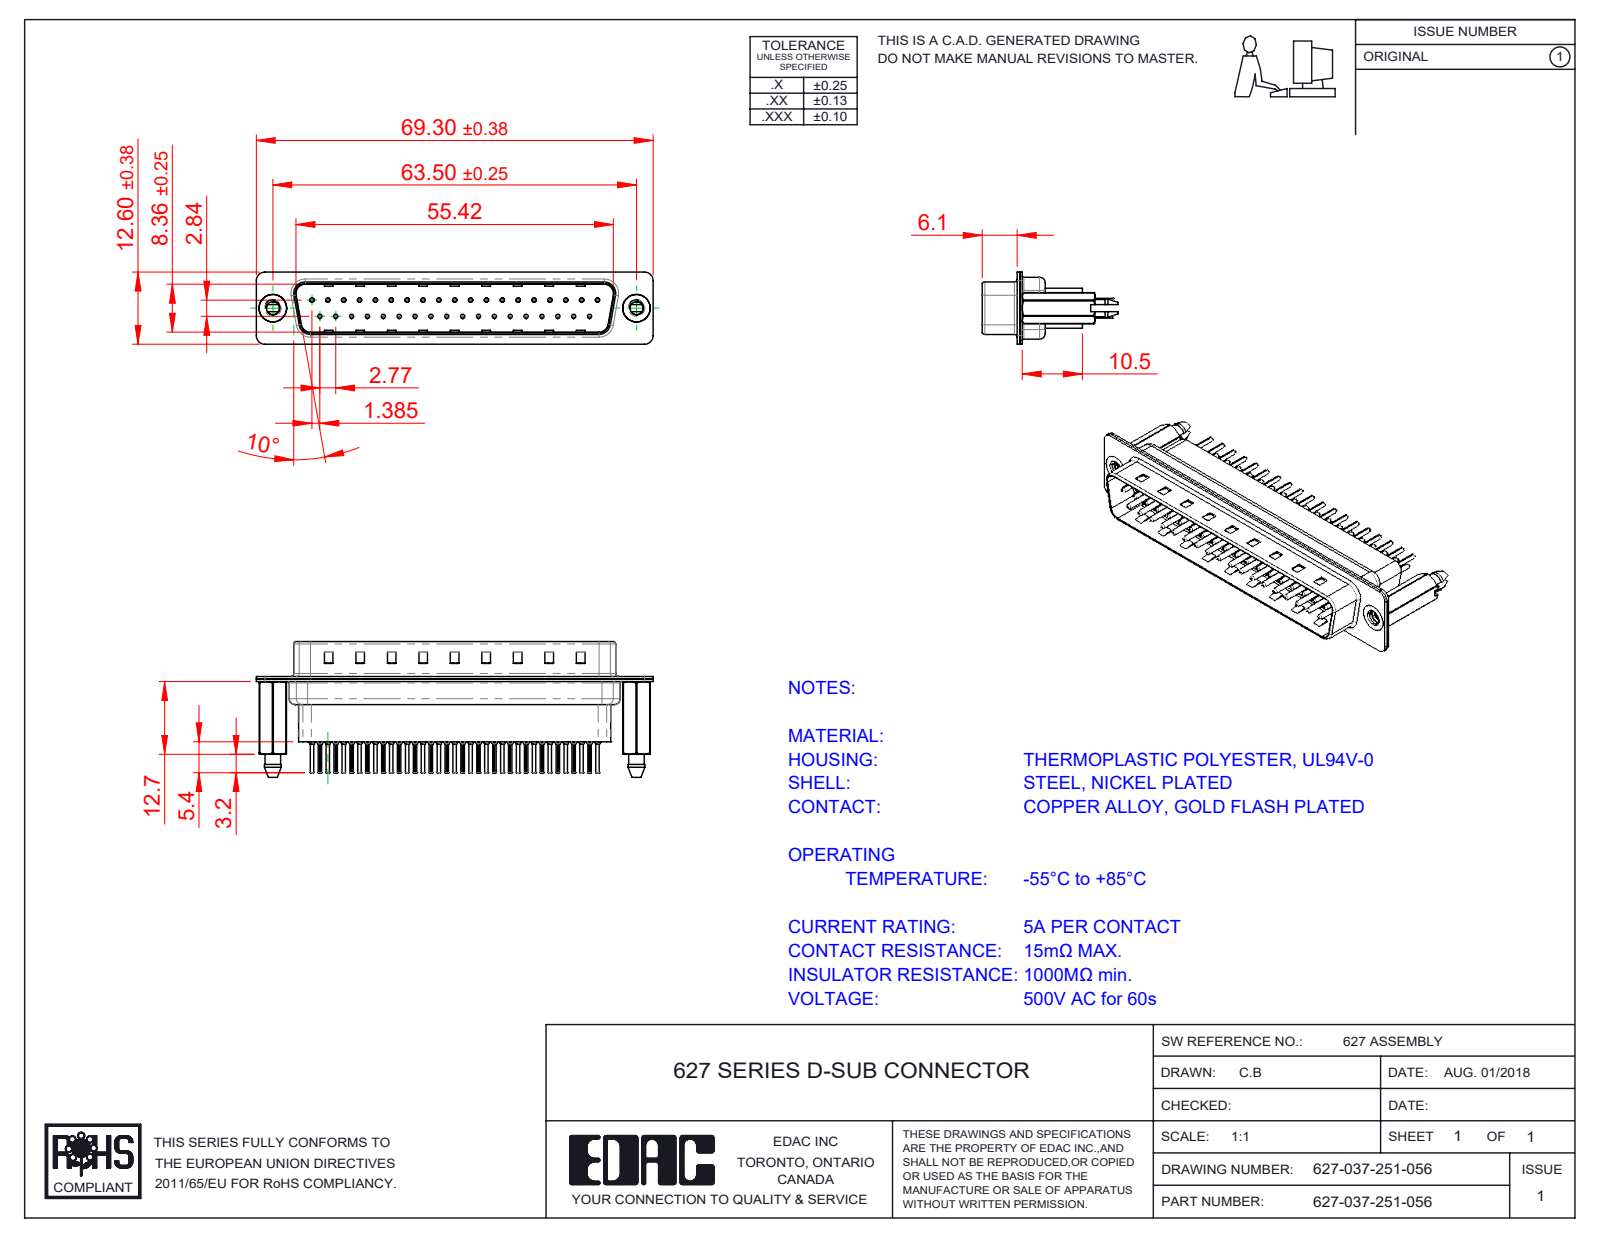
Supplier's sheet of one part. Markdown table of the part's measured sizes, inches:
| quantity | value |
| --- | --- |
| part name | 627 Contact Row 1_41; 627 Contact Row 2_41; 627 Shell Rear_37 Contacts; 627 4-40 Threaded Boardlock_HP51 (+3 more) |
| STEP written by | SolidWorks 2020 (CONFIG_CONTROL_DESIGN) |
| units | inches |
| bodies | 42 solids, 4146 faces (1123 planar, 1576 cylindrical, 1447 other) |
| overall size | 2.728 × 0.929 × 0.496 |
| volume | 0.344 in³ |
| surface area | 22.39 in² |
| round holes (diameter × count) | 0.008 × 37, 0.014 × 37, 0.043 × 37, 0.063 × 37, 0.089 × 2, 0.157 × 2, 0.189 × 2 |
| round bosses / shafts (diameter × count) | 0.079 × 37, 0.059 × 37, 0.03 × 37, 0.024 × 37, 0.193 × 2 |
| partial cylindrical surfaces (radius × count) | 0.004 × 74, 0.059 × 18, 0.079 × 12, 0.063 × 10, 0.02 × 8, 0.01 × 4, 0.024 × 4, 0.026 × 4 |
| main face-to-face distances | 0.016, 0.032, 0.377, 0.027, 0.302, 0.018, 0.059, 0.043, 0.318, 0.345 |
| hole center spacings | 0.124, 0.109, 0.218, 0.327, 0.198, 0.398, 0.436, 0.503 |
